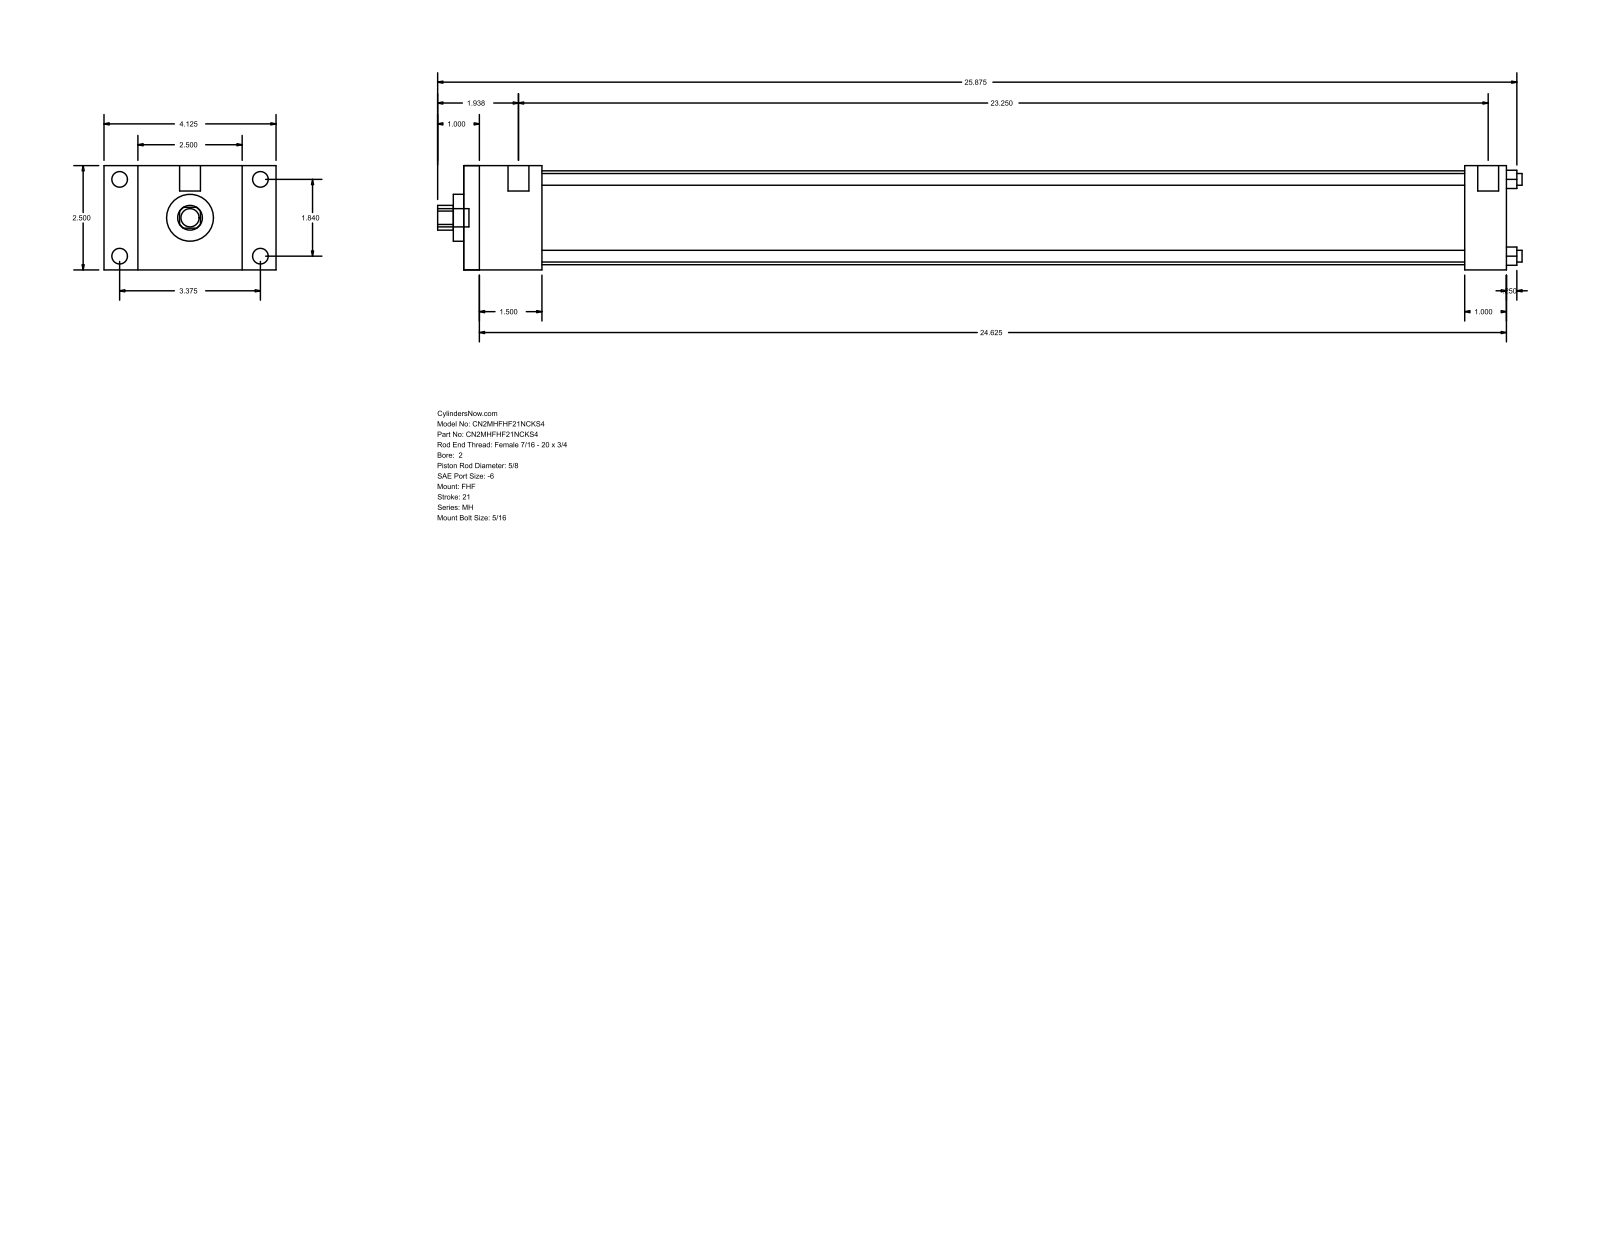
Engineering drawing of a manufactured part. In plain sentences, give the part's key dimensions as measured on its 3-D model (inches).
The part is named "MH_FHF__0200_0.625". Its 3-D file was written by "GSSL Pune (CONFIG_CONTROL_DESIGN)". It is 0 solids with 88 faces: 60 planar, 28 cylindrical and 0 other. Overall it measures 26 by 4.125 by 2.5 inches. Round holes: 4 of diameter 0.281, 1 of diameter 0.625, 1 of diameter 1.125, 1 of diameter 2.25. Round bosses or shafts: 4 of diameter 0.375, 4 of diameter 0.219, 2 of diameter 0.5, 1 of diameter 0.437. Partial cylindrical surfaces (rounded edges, fillets, slot ends): 1 of radius 0.297. The main face-to-face distances are 2.5, 1.875, 25, 23.125, 0.813, 3.313, 4.125, 1, 24, 22.125. The hole center spacings are 1.301, 1.84, 2.602.
